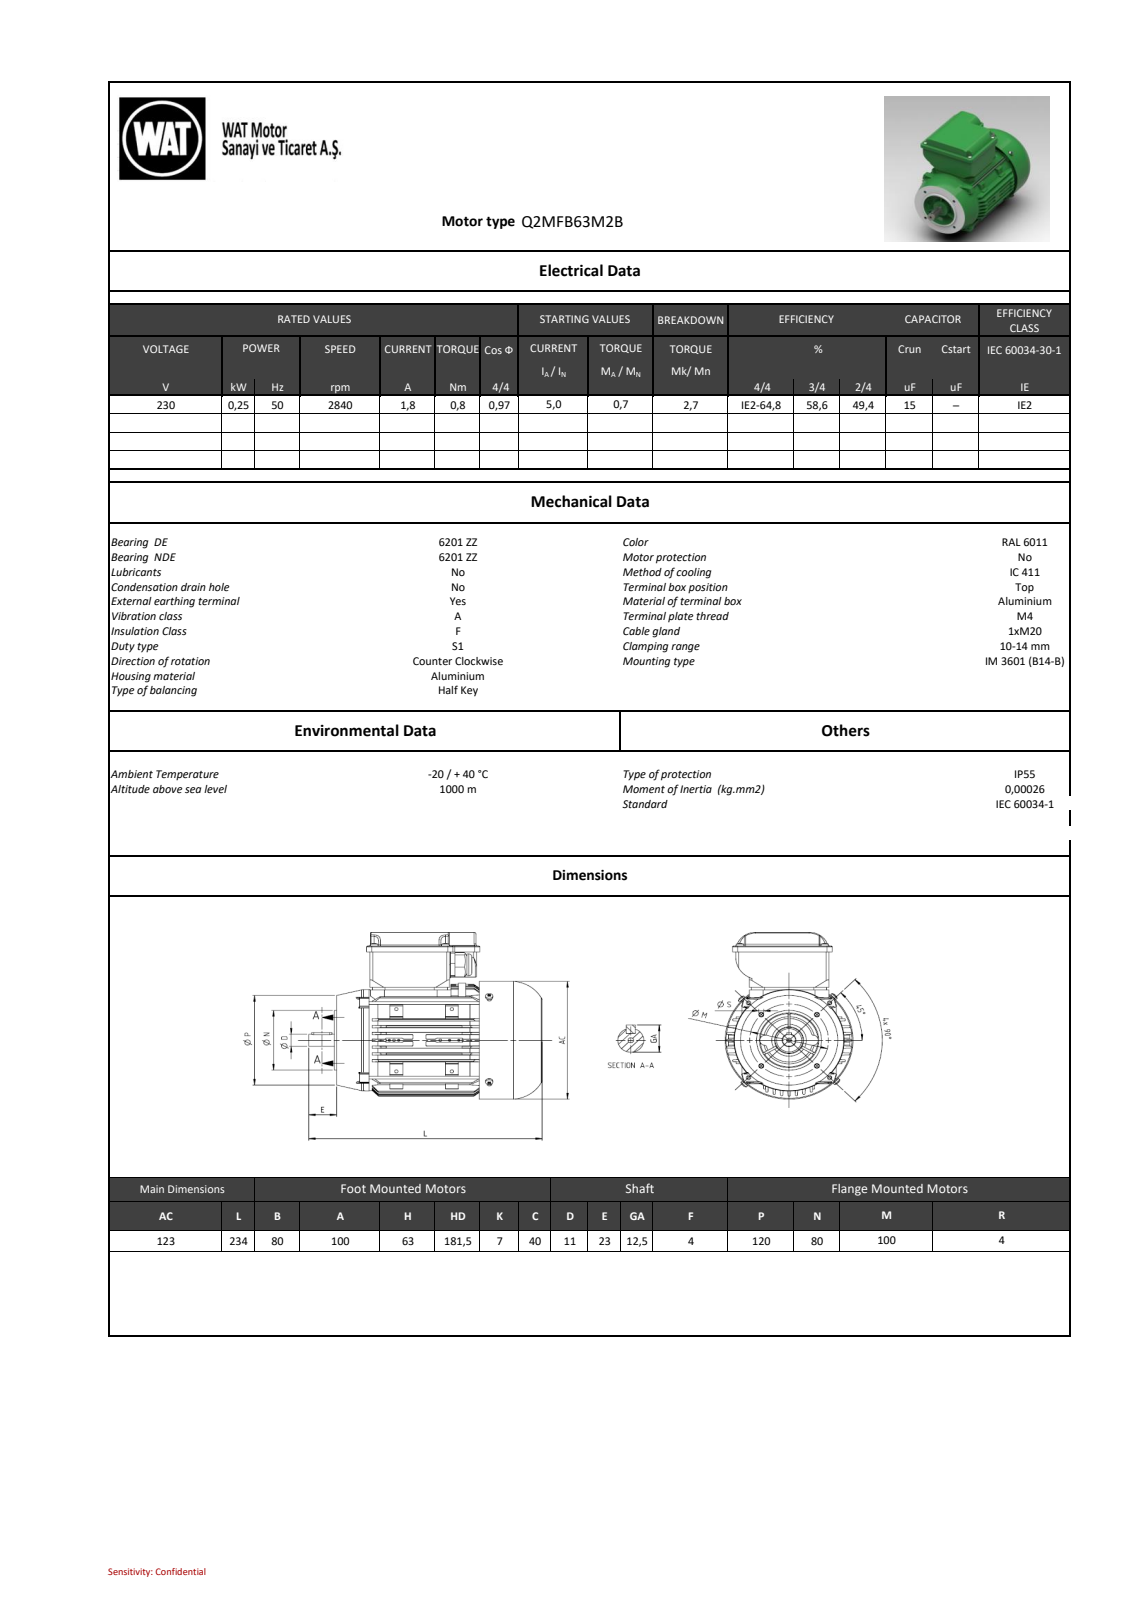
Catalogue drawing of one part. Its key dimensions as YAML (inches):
part_name: "BY6424130xx_004-TKK_QM63-80; BY6434017xx_004-TK_QM63-80; BY6424189xx_005-MOTOR_KAPAGI_QS63FB_ISLEME; BY6423003xx_006-FAN_KAPAGI_QS63 (+6 more)"
step_written_by: "SIEMENS PLM Software NX2206.8101 (AUTOMOTIVE_DESIGN)"
units: inches
bodies: {solids: 34, faces: 2219, planar: 1119, cylindrical: 738, other: 362}
overall_size: [9.192, 7.087, 4.843]
volume: 37.82
surface_area: 642.7
round_holes:
  - {diameter: 0.144, count: 10}
  - {diameter: 0.157, count: 8}
  - {diameter: 0.177, count: 8}
  - {diameter: 0.098, count: 6}
  - {diameter: 0.13, count: 5}
  - {diameter: 0.183, count: 4}
  - {diameter: 0.189, count: 4}
  - {diameter: 0.236, count: 4}
  - {diameter: 0.118, count: 3}
  - {diameter: 0.197, count: 1}
  - {diameter: 0.315, count: 1}
  - {diameter: 0.394, count: 1}
round_bosses_or_shafts:
  - {diameter: 0.315, count: 8}
  - {diameter: 0.157, count: 8}
  - {diameter: 0.118, count: 8}
  - {diameter: 0.189, count: 4}
  - {diameter: 4.843, count: 1}
  - {diameter: 4.724, count: 1}
  - {diameter: 3.15, count: 1}
  - {diameter: 0.995, count: 1}
partial_cylinders:
  - {radius: 0.02, count: 210}
  - {radius: 0.039, count: 77}
  - {radius: 0.079, count: 67}
  - {radius: 0.197, count: 26}
  - {radius: 0.118, count: 21}
  - {radius: 0.098, count: 20}
  - {radius: 0.217, count: 9}
  - {radius: 0.059, count: 8}
face_to_face_distances: [0.118, 0.177, 0.276, 1.101, 0.059, 5.807, 0.039, 1.104, 7.146, 0.271]
hole_center_spacings: [2.165, 2.126, 2.48, 2.634, 2.784, 3.267, 0.394, 1.713]
